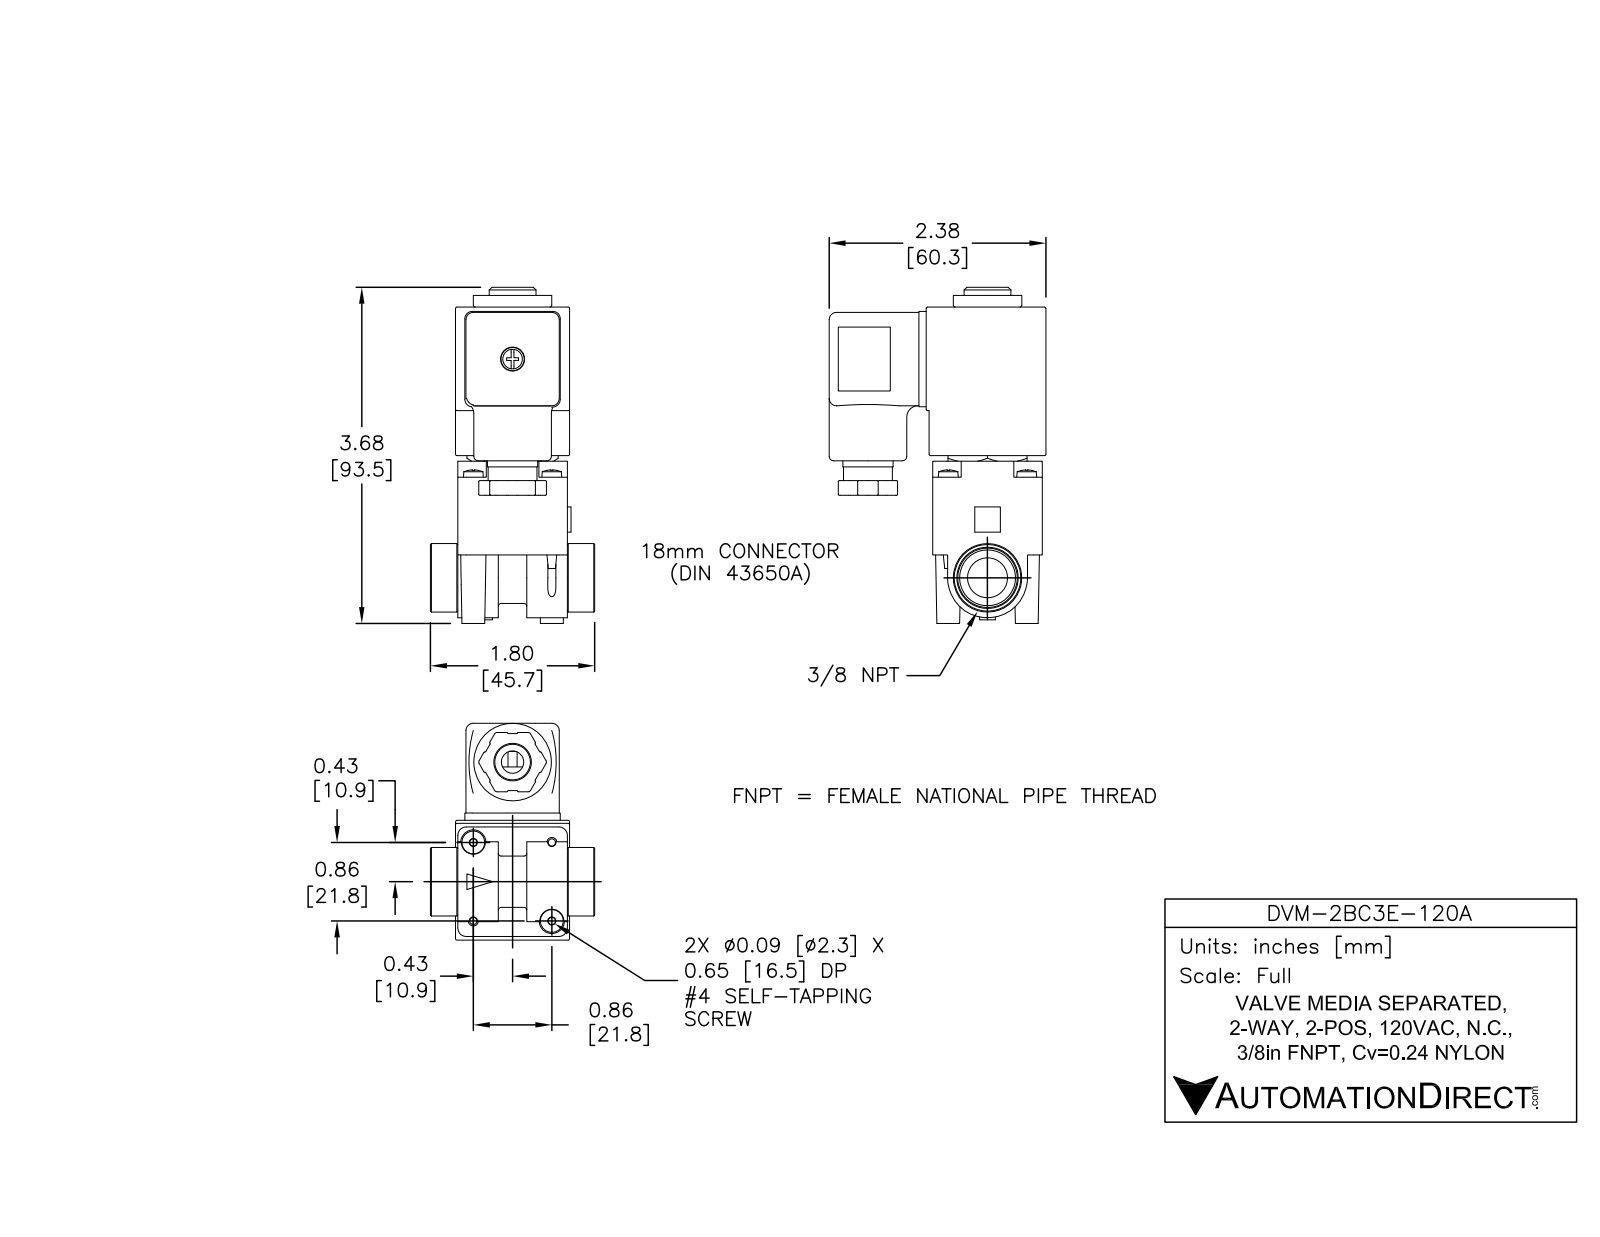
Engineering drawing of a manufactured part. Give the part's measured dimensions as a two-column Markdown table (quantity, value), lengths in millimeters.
| quantity | value |
| --- | --- |
| part name | DVM-2BC3E-120A |
| STEP written by | SolidWorks 2015 (AUTOMOTIVE_DESIGN) |
| units | millimeters |
| bodies | 14 solids, 1775 faces (895 planar, 351 cylindrical, 529 other) |
| overall size | 93.5 × 60.3 × 45.7 |
| volume | 83 820 mm³ |
| surface area | 43 890 mm² |
| round holes (diameter × count) | 2.8 × 4, 1.5 × 2, 2.3 × 2, 8 × 2, 3 × 1, 4 × 1, 5.2 × 1, 6.2 × 1, 6.4 × 1, 6.7 × 1, 9.9 × 1, 10.2 × 1 |
| round bosses / shafts (diameter × count) | 5.5 × 4, 3.2 × 4, 22.2 × 1, 22.2 × 1, 21.6 × 1, 20.5 × 1, 17.3 × 1, 13.6 × 1 |
| partial cylindrical surfaces (radius × count) | 0.3 × 54, 0.1 × 21, 0.4 × 17, 0.5 × 12, 0.8 × 12, 0.8 × 12, 2 × 12, 1.3 × 8 |
| main face-to-face distances | 31.8, 30.5, 4.1, 27.6, 1.2, 3.5, 24.7, 31.1, 24.5, 1 |
| hole center spacings | 15.4, 15.4, 17.4, 21.8, 21.8, 24.9, 30.9, 37 |
